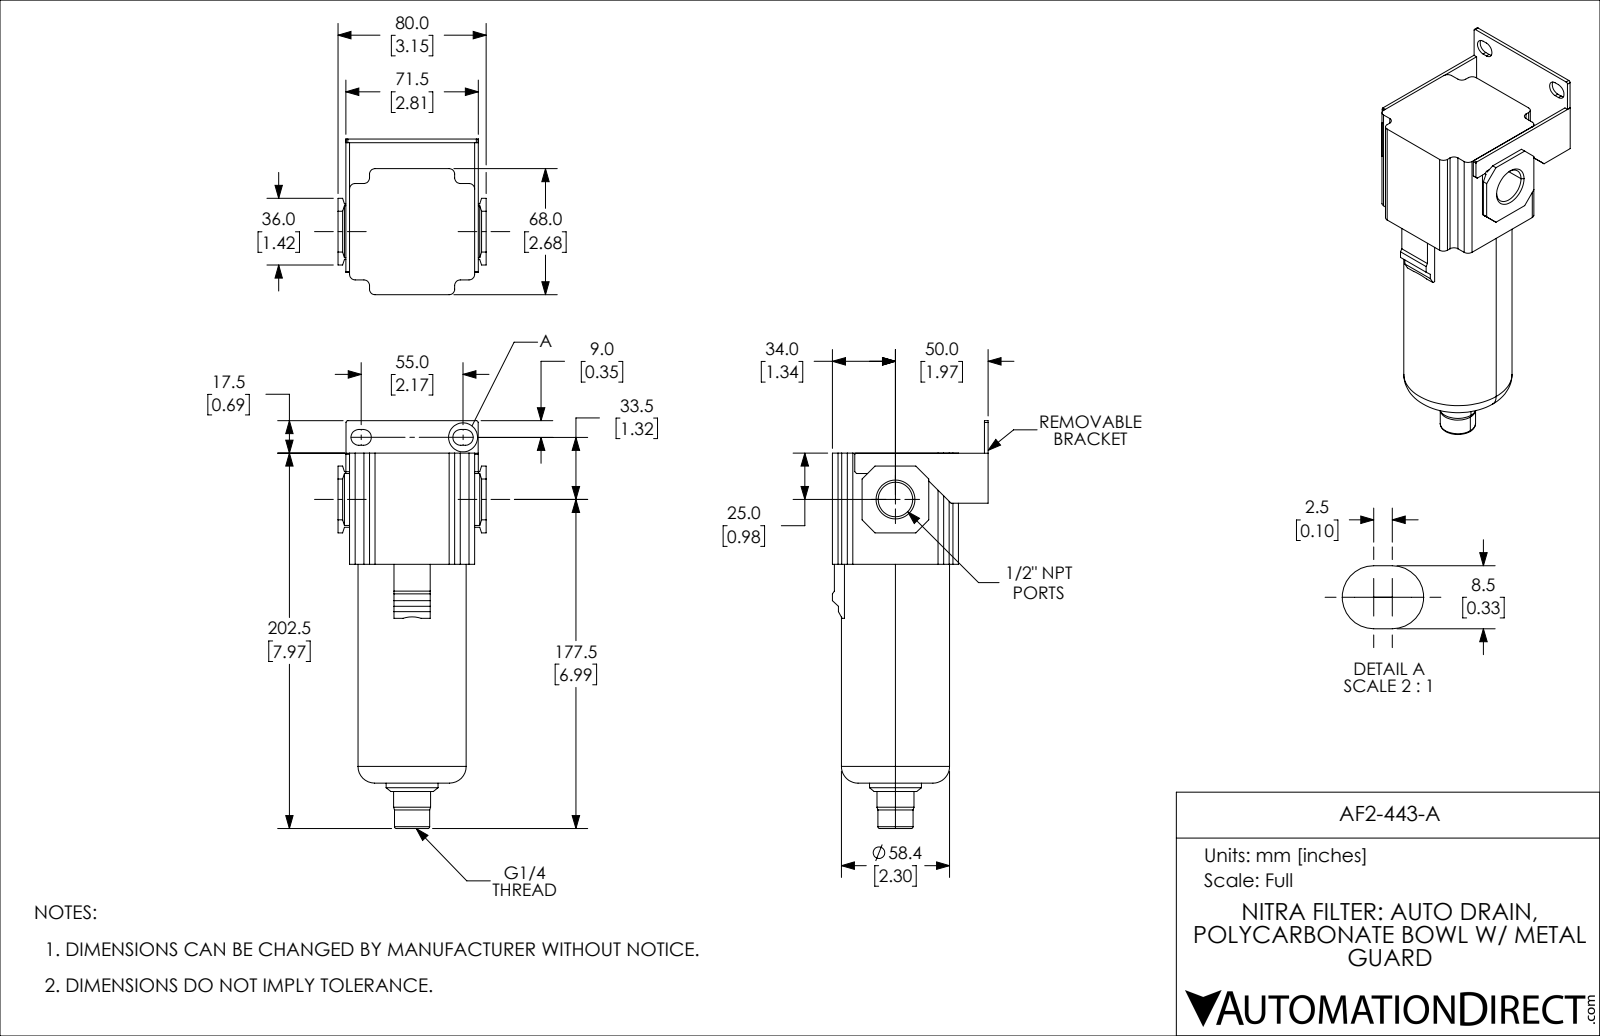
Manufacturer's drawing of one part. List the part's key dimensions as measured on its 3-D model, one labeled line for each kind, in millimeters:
Part name (STEP PRODUCT): AF2-443-A
STEP written by: SolidWorks 2019 (CONFIG_CONTROL_DESIGN)
Units: millimetres
Bodies: 1 solid, 136 faces (90 planar, 32 cylindrical, 14 other)
Overall size (bounding box): 220 × 84 × 80
Volume: 589 844 mm³ · Surface area: 61 015 mm²
Round holes (diameter × count): ⌀8.57 ×1, ⌀18.63 ×1
Round bosses / shafts (diameter × count): ⌀58.4 ×1, ⌀28 ×1, ⌀20 ×1, ⌀19 ×1
Partial cylindrical surfaces — rounded edges, fillets, slot ends (radius × count): R3 ×12, R4.25 ×4, R1 ×2
Main face-to-face distances: 2, 16, 60, 68, 84, 82, 69.5, 14, 67.5, 4.25
